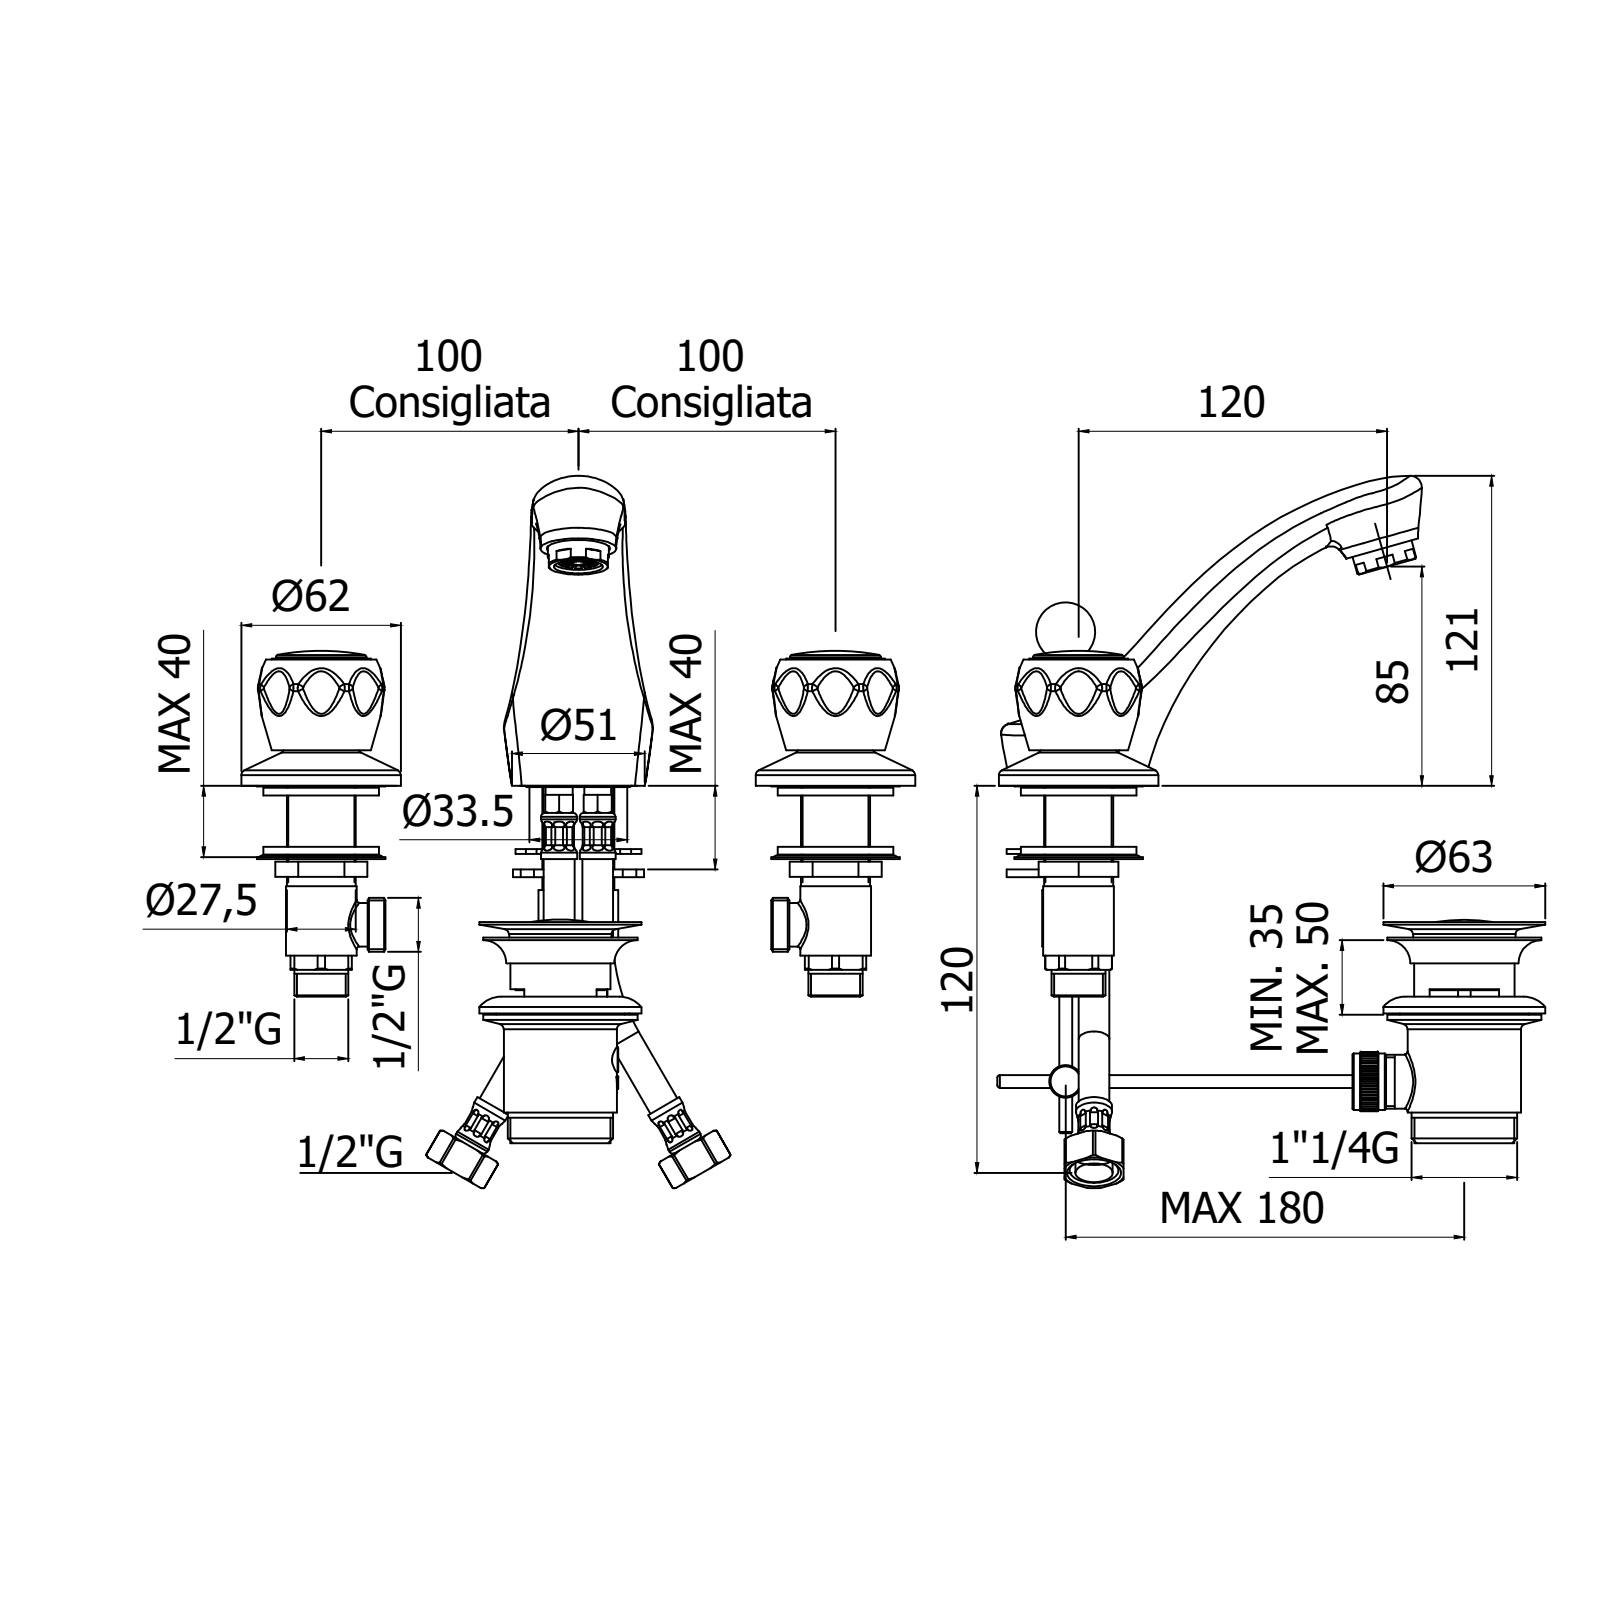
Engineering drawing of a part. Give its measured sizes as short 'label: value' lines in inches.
name: DA056CR
written by: CREO PARAMETRIC BY PTC INC, 2020044 (CONFIG_CONTROL_DESIGN)
unit: in
bodies: 4 solids, 323 faces (46 planar, 64 cylindrical, 213 other)
size: 10.315 × 6.474 × 4.854
volume: 16.4 in³; area: 119.1 in²
holes: 2× ⌀0.197, 2× ⌀0.354, 2× ⌀0.433, 1× ⌀0.205, 1× ⌀0.63, 1× ⌀0.827, 1× ⌀0.906, 1× ⌀1.654, 1× ⌀1.89
bosses: 2× ⌀2.441, 2× ⌀1.516, 1× ⌀0.937, 1× ⌀0.866, 1× ⌀0.315, 1× ⌀0.197
rounds: 16× R0.839, 4× R0.059, 2× R0.197, 2× R0.295
face distances: 0.118, 0.079, 0.157, 0.543, 0.236, 1.933, 1.39, 0.386, 1.776, 1.949
hole spacings: 0.378, 0.461, 0.524, 0.559, 0.606, 0.938, 0.197, 0.591
